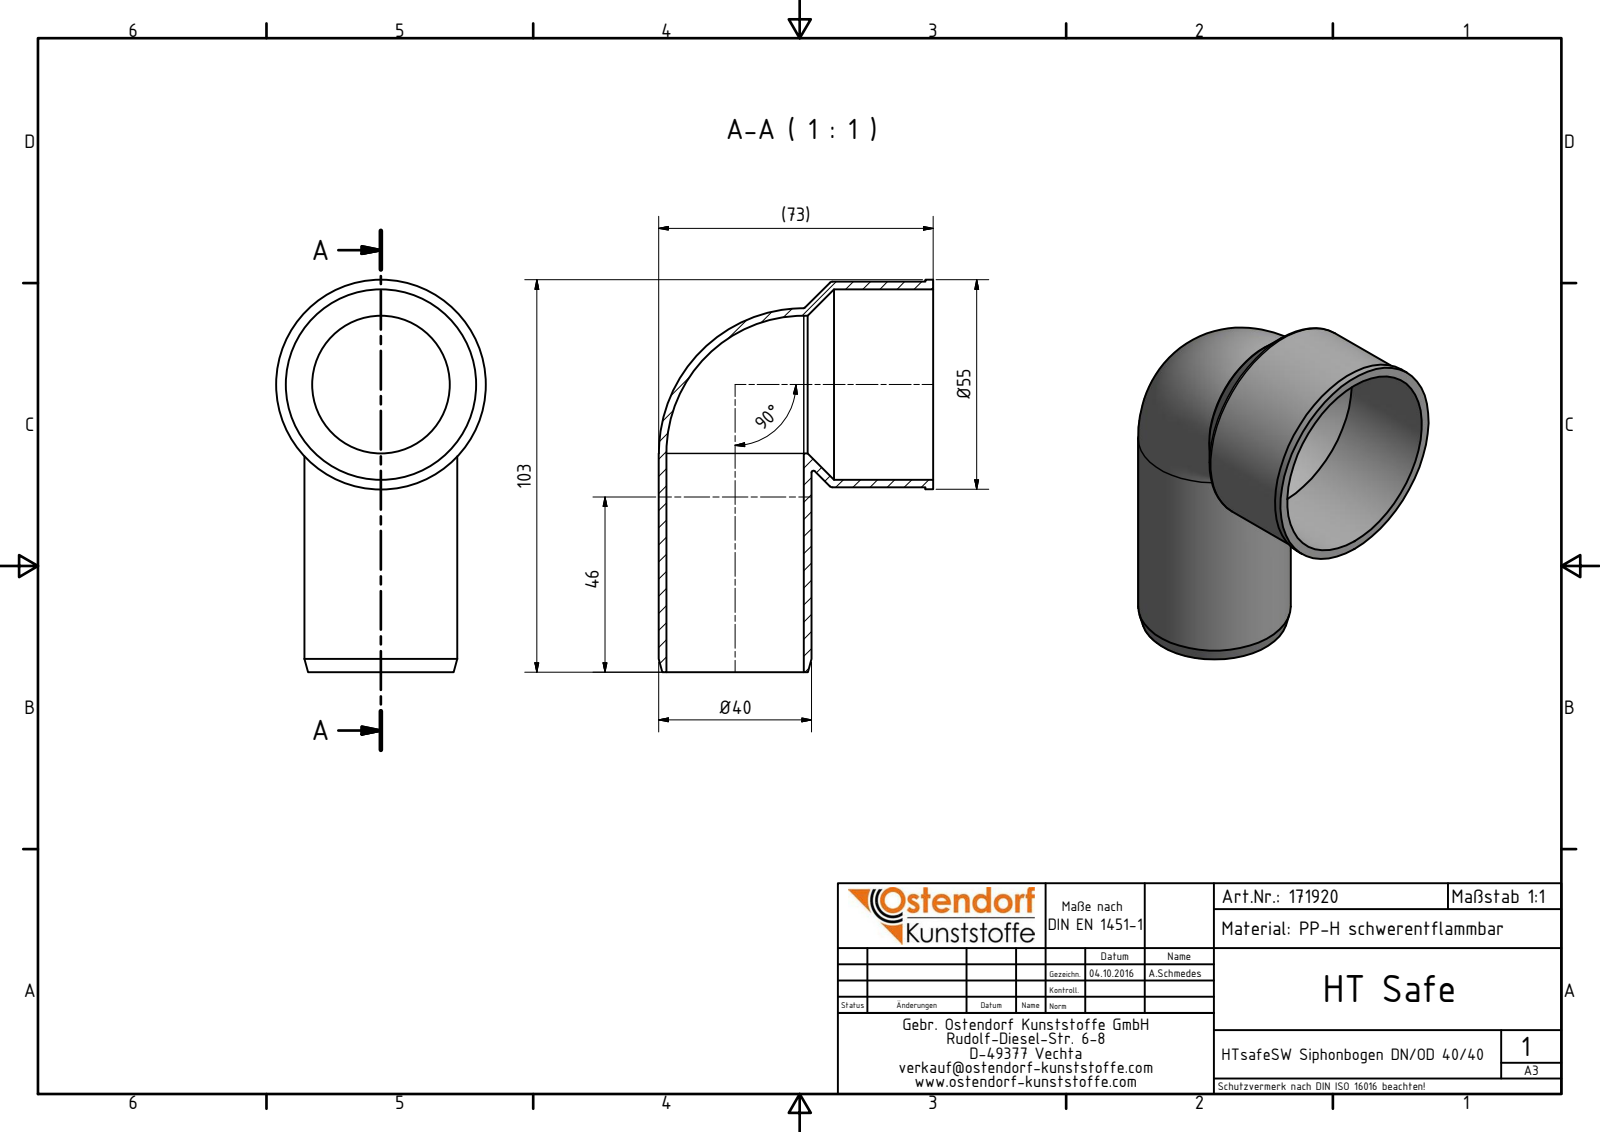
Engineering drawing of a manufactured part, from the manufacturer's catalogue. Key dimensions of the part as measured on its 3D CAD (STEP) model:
Part name (STEP PRODUCT): 171920 HTsafeSW DN_OD 40_40
STEP written by: Autodesk Inventor 2016 (AUTOMOTIVE_DESIGN)
Units: millimetres
Bodies: 1 solid, 17 faces (3 planar, 6 cylindrical, 8 other)
Overall size (bounding box): 103 × 72.05 × 55
Volume: 31 567 mm³ · Surface area: 32 729 mm²
Round holes (diameter × count): ⌀36.1 ×2, ⌀50 ×1
Round bosses / shafts (diameter × count): ⌀55 ×1, ⌀54 ×1, ⌀40.1 ×1
Main face-to-face distances: 2
